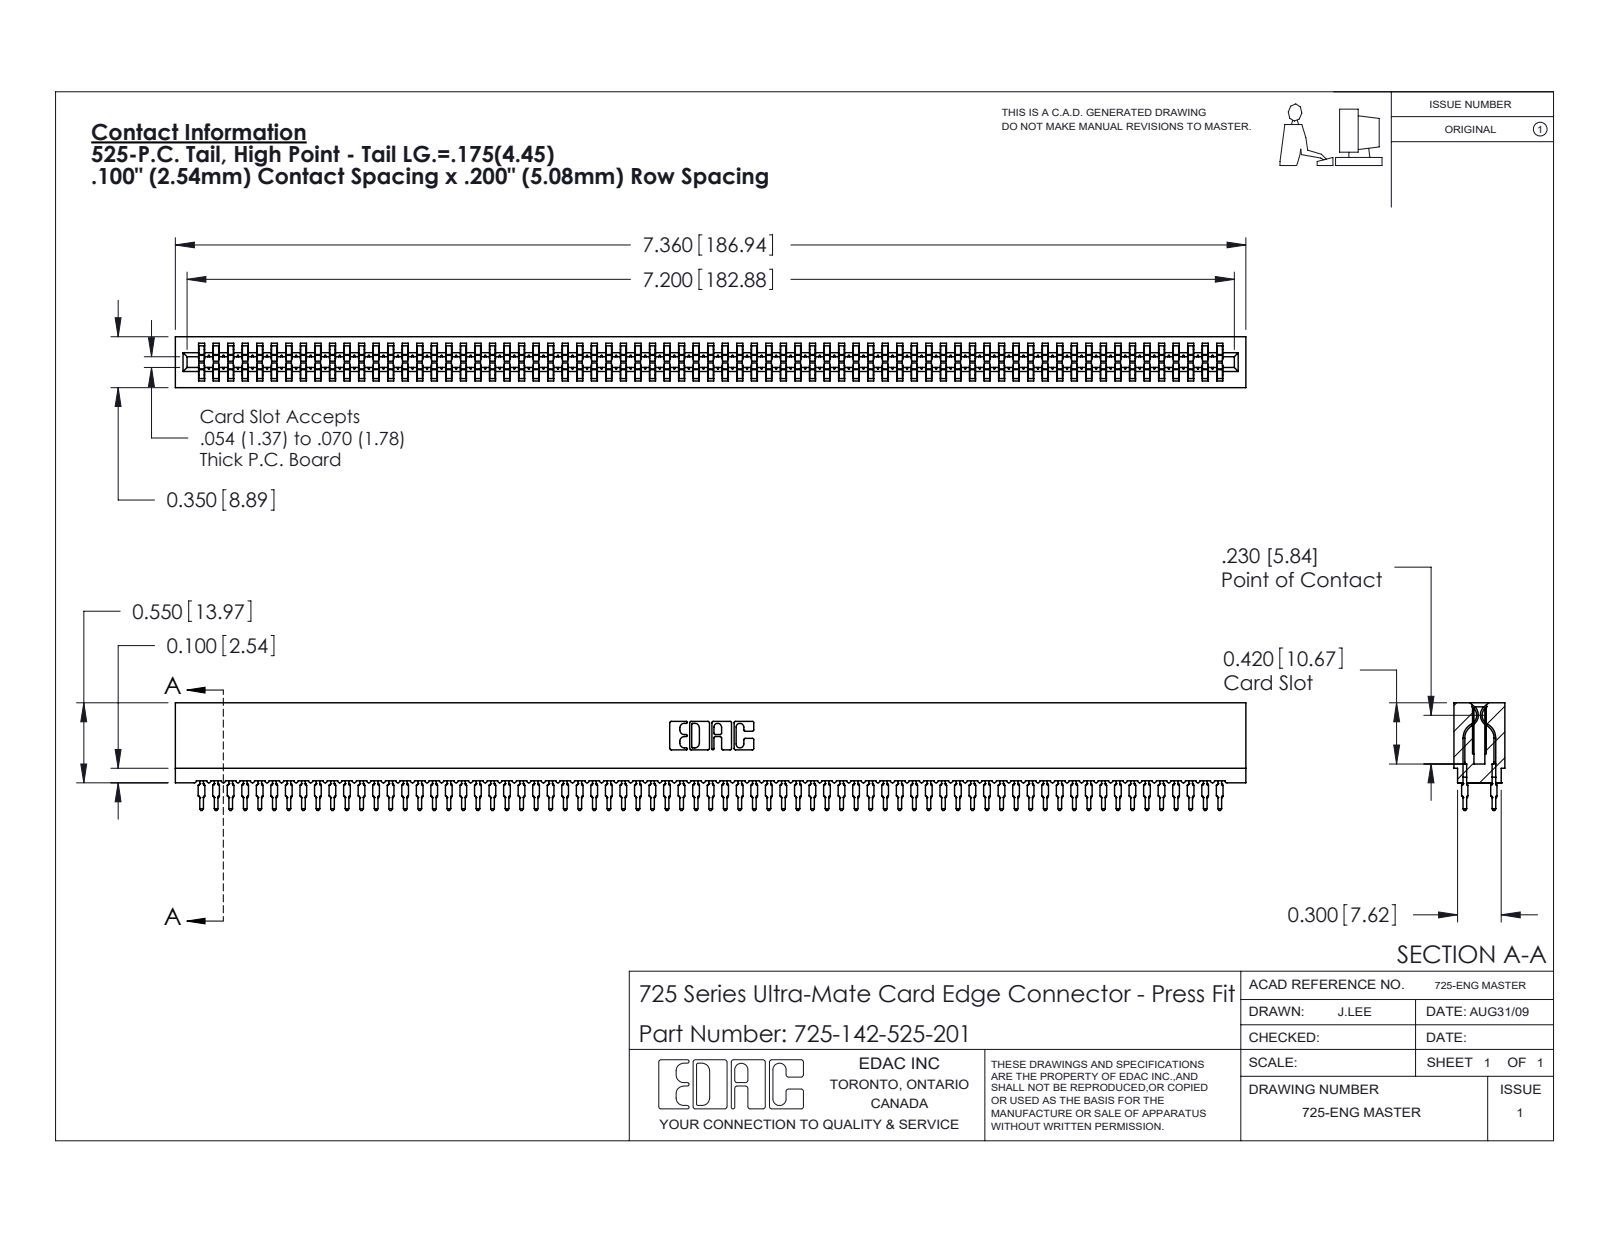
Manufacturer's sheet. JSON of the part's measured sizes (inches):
{"part_name": "725-142-525-201; 745-292-001_525; 725 Part_Insulator Option - 01", "step_written_by": "SolidWorks 2020 (CONFIG_CONTROL_DESIGN)", "units": "inches", "bodies": {"solids": 143, "faces": 12804, "planar": 6587, "cylindrical": 2525, "other": 3692}, "overall_size": [7.36, 0.741, 0.35], "volume_in3": 0.893, "surface_area_in2": 48.76, "partial_cylinders_radius": [[0.021, 284], [0.015, 142], [0.01, 22], [0.005, 8], [0.011, 8], [0.007, 6], [0.031, 6], [0.026, 3]], "face_to_face_distances": [0.063, 0.287, 0.35, 0.2, 0.212, 0.138, 0.076, 0.149, 0.045, 0.305]}
